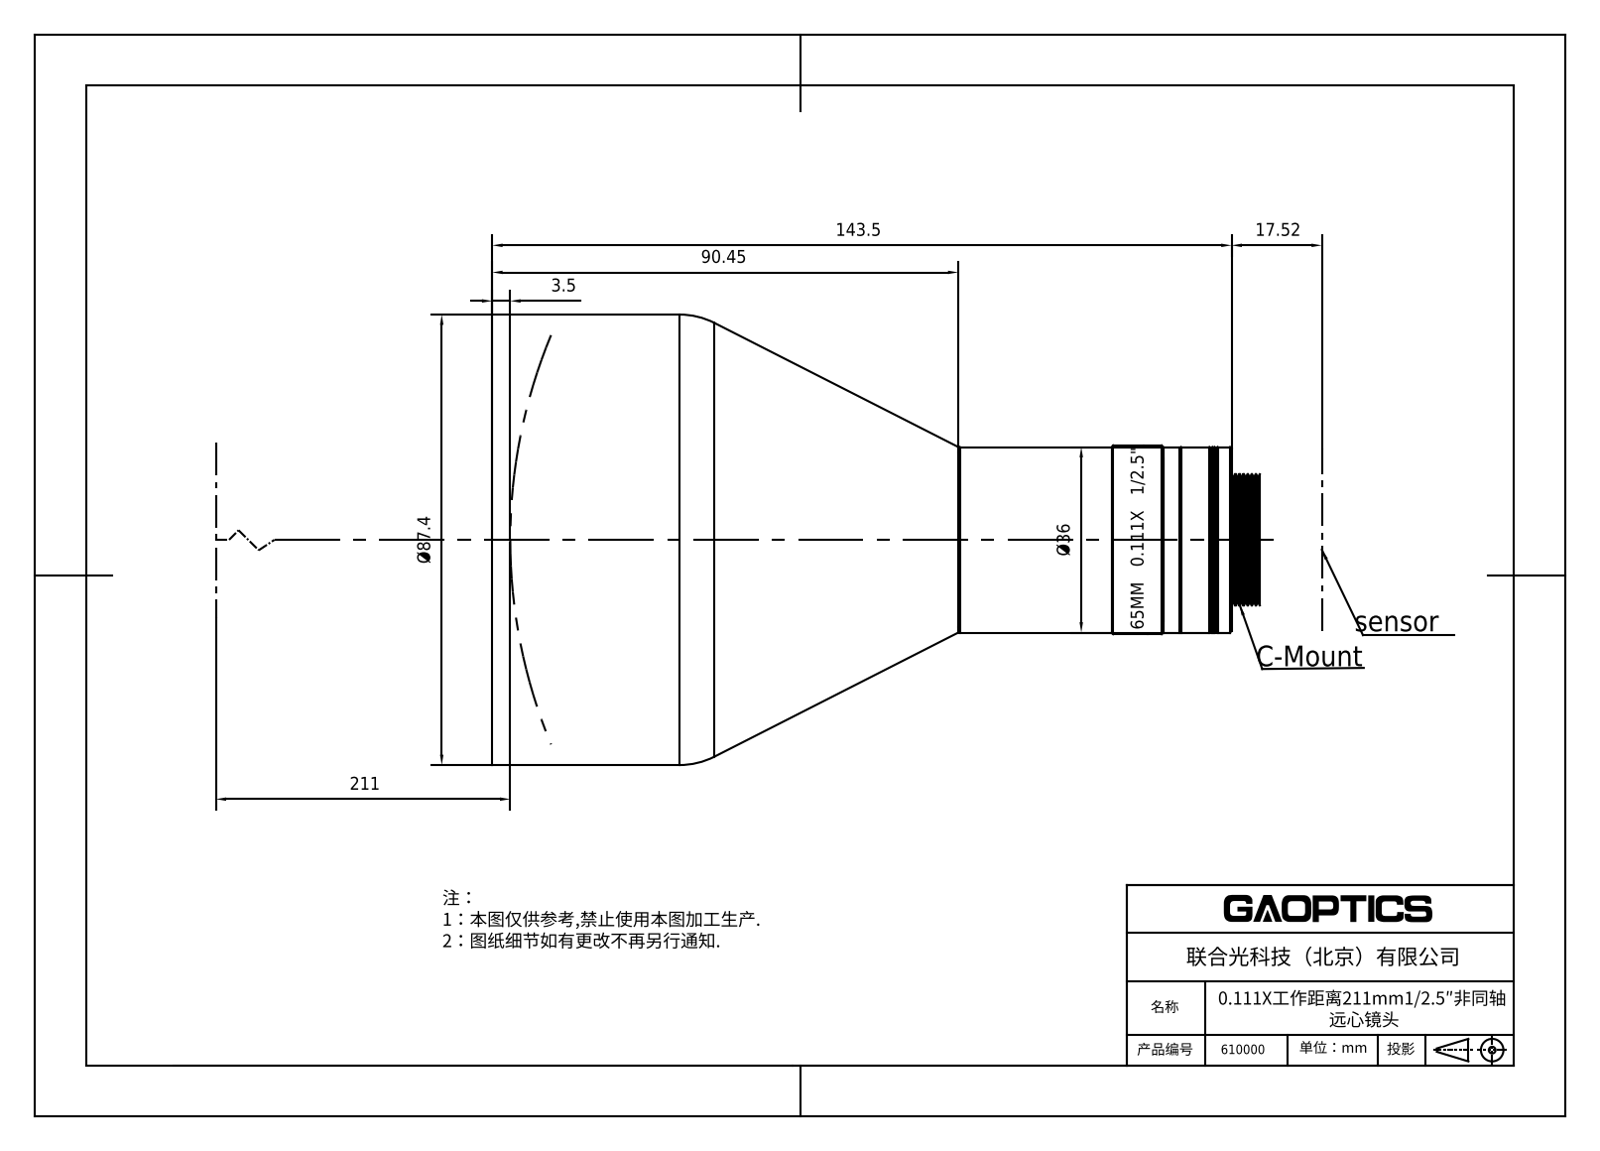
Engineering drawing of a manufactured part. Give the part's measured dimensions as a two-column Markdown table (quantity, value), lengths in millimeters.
| quantity | value |
| --- | --- |
| part name | 610000 |
| STEP written by | SolidWorks 2020 (CONFIG_CONTROL_DESIGN) |
| units | millimeters |
| bodies | 0 solids, 453 faces (100 planar, 113 cylindrical, 240 other) |
| overall size | 148.78 × 87.4 × 87.4 |
| round holes (diameter × count) | 2.2 × 3, 3 × 3, 11.44 × 1, 16.8 × 1, 17.8 × 1, 21.9 × 1, 24.6 × 1, 25.8 × 1, 33 × 1, 35 × 1, 76.4 × 1, 87.4 × 1 |
| round bosses / shafts (diameter × count) | 82 × 1, 80.4 × 1, 36.6 × 1, 36 × 1, 31.6 × 1, 25.4 × 1, 24.54 × 1, 24.3 × 1 |
| partial cylindrical surfaces (radius × count) | 0.5 × 2, 18.2 × 1 |
| main face-to-face distances | 26.99, 6, 3, 122.74, 95.75, 128.79, 129.79, 102.8, 7.05, 132.79 |
| hole center spacings | 14.5, 25.12 |
